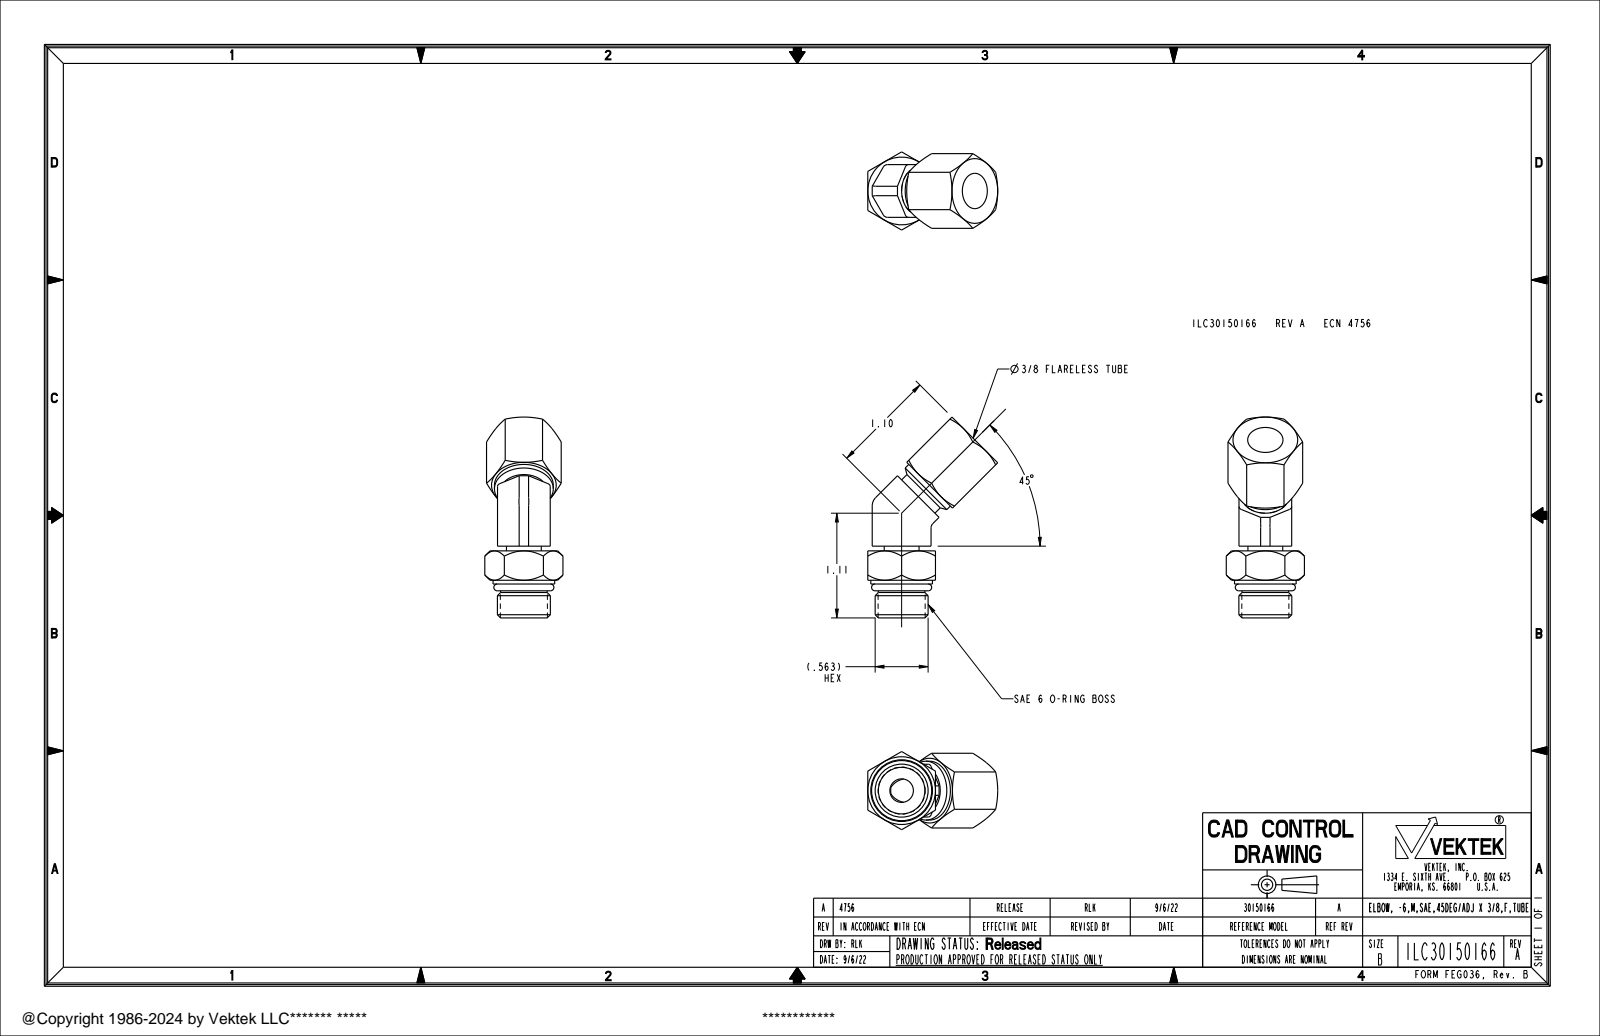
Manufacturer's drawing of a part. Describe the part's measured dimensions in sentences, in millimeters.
The part is named "ILC30150166". Its 3-D file was written by "CREO PARAMETRIC BY PTC INC, 2021164 (AUTOMOTIVE_DESIGN)". It is 2 solids with 115 faces: 35 planar, 38 cylindrical and 42 other. Overall it measures 54.2 by 35.1 by 21.1 millimeters. Its volume is 9 670 cubic millimeters and its surface area 6 018 square millimeters. Round holes: 2 of diameter 6.4, 1 of diameter 9.5. Round bosses or shafts: 2 of diameter 12.7, 1 of diameter 16.6, 1 of diameter 15.9, 1 of diameter 14.3, 1 of diameter 12.5, 1 of diameter 9.4. Partial cylindrical surfaces (rounded edges, fillets, slot ends): 8 of radius 1.3, 3 of radius 1.5, 3 of radius 3.2. The main face-to-face distances are 17.4, 18.3, 17.4, 14.2, 1.3, 8.9, 10.2, 9.1, 18.1, 19.4.
